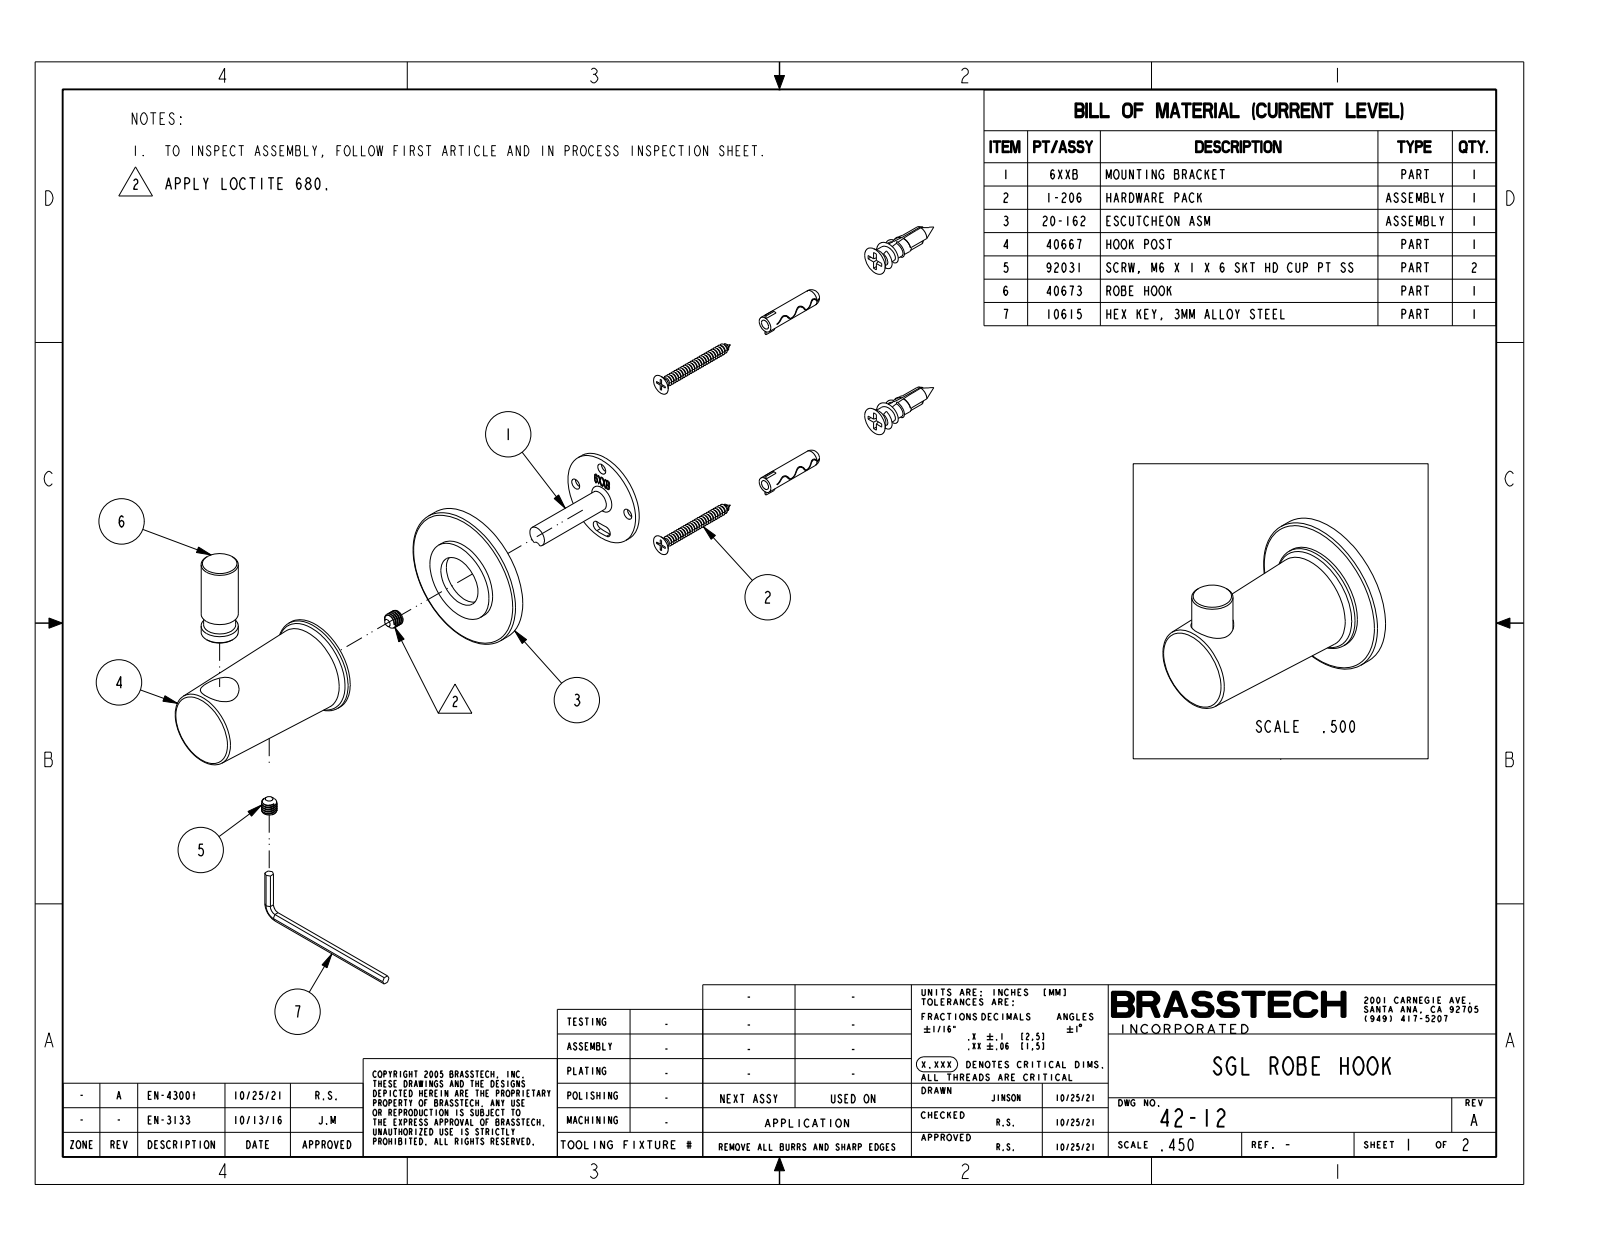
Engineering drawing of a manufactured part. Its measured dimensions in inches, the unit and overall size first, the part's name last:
Units: inches
Overall size (bounding box): 2.657 × 2.2 × 2.2
Round holes (diameter × count): ⌀1.3 ×1
Round bosses / shafts (diameter × count): ⌀2.2 ×1, ⌀1.5 ×1, ⌀1.275 ×1, ⌀0.567 ×1
Main face-to-face distances: 0.187, 2.657, 2.47, 0.197, 2.46, 0.267, 0.08, 0.07, 2.39
Volume: 3.959 in³ · Surface area: 20.47 in²
Bodies: 1 solid, 28 faces (6 planar, 10 cylindrical, 12 other)
Part name (STEP PRODUCT): 42-12
STEP written by: CREO PARAMETRIC BY PTC INC, 2018400 (CONFIG_CONTROL_DESIGN)
